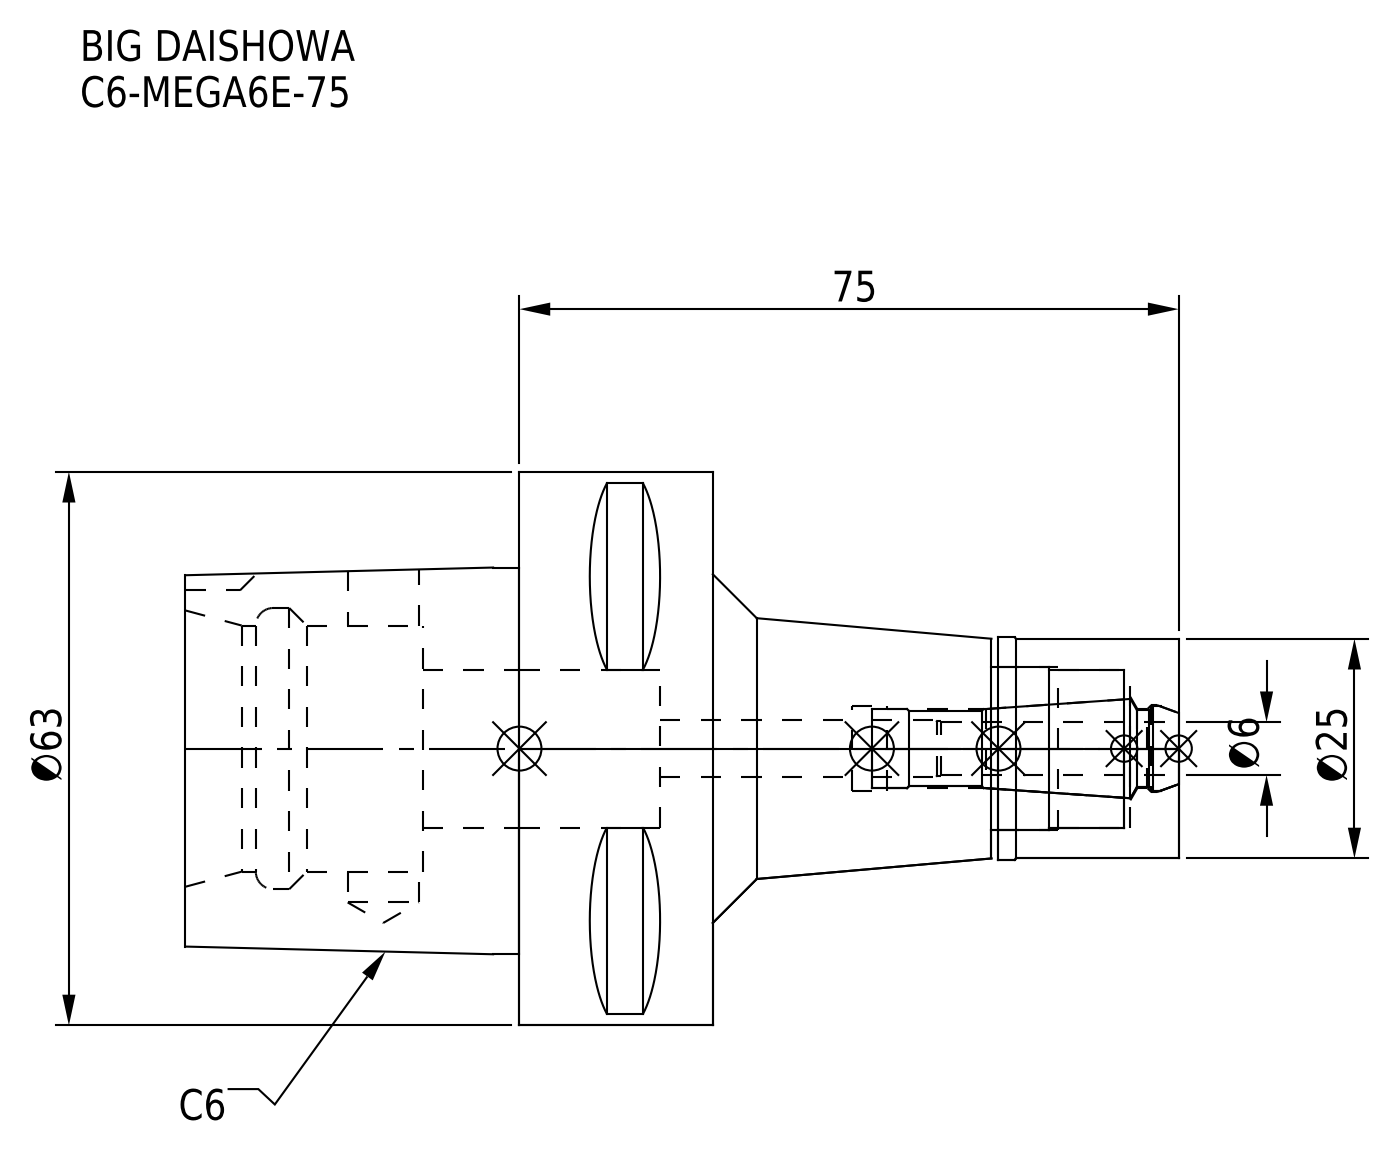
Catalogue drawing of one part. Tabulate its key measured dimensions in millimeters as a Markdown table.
| quantity | value |
| --- | --- |
| part name | C6-MEGA6E-75-060_ASM.stp; C6-MEGA6E-75_1.stp; C6-MEGA6E-75-060-FreeParts; DXF_TEMP_ASSY_ASM_4_ASM.stp (+3 more) |
| STEP written by | SolidWorks 2019 (CONFIG_CONTROL_DESIGN) |
| units | millimeters |
| bodies | 2 solids, 97 faces (36 planar, 37 cylindrical, 24 other) |
| overall size | 113 × 63 × 63 |
| volume | 123 786 mm³ |
| surface area | 28 138 mm² |
| round holes (diameter × count) | 6.4 × 1, 8.1 × 1, 9 × 1, 9.6 × 1, 9.9 × 1, 18 × 1, 18.5 × 1, 28 × 1, 32 × 1 |
| round bosses / shafts (diameter × count) | 63 × 1, 25.3 × 1, 25 × 1 |
| partial cylindrical surfaces (radius × count) | 5 × 1 |
| main face-to-face distances | 22, 27, 60, 38, 53, 75, 113, 86, 33, 11 |
